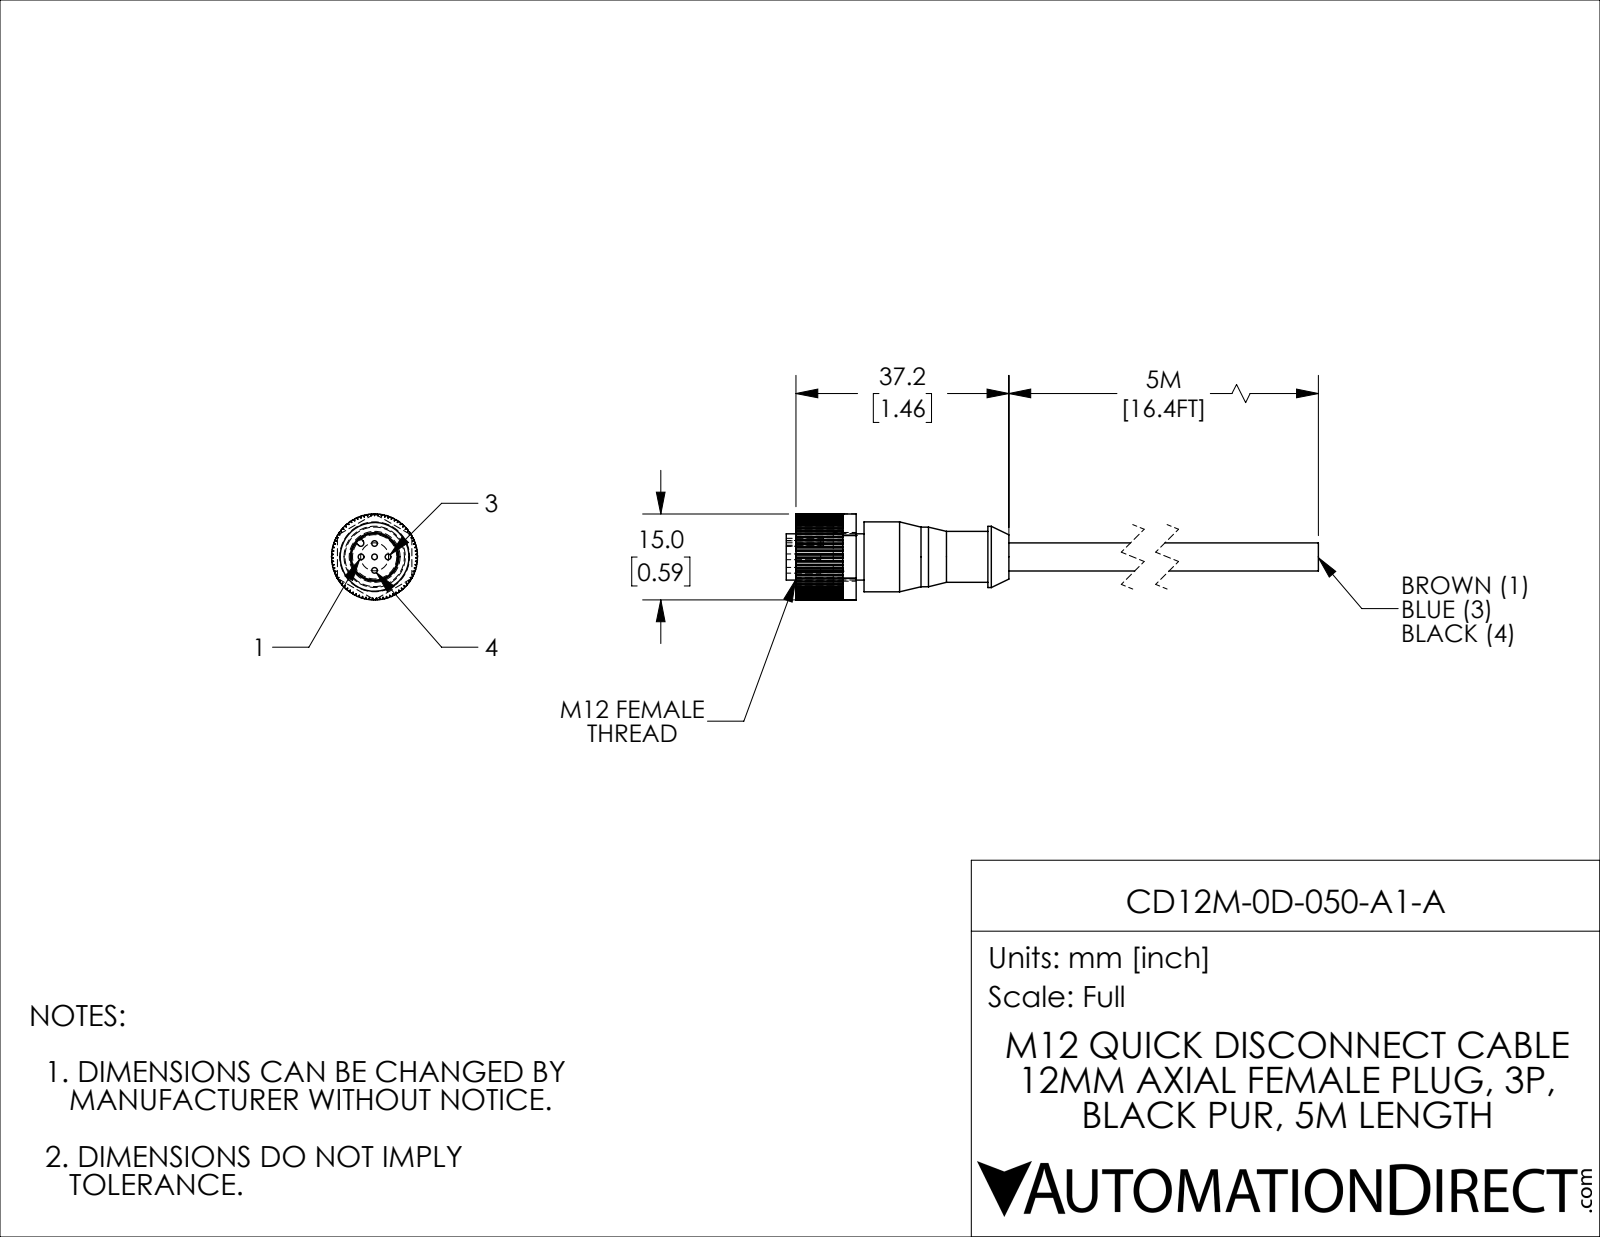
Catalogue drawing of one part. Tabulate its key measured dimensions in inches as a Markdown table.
| quantity | value |
| --- | --- |
| part name | CD12M-0D-050-A1-A |
| STEP written by | SolidWorks 2021 (CONFIG_CONTROL_DESIGN) |
| units | inches |
| bodies | 4 solids, 308 faces (195 planar, 107 cylindrical, 6 other) |
| overall size | 5.469 × 0.591 × 0.591 |
| volume | 0.336 in³ |
| surface area | 6.948 in² |
| round holes (diameter × count) | 0.039 × 5, 0.335 × 1, 0.472 × 1 |
| round bosses / shafts (diameter × count) | 0.48 × 1, 0.421 × 1, 0.409 × 1, 0.35 × 1, 0.319 × 1, 0.193 × 1 |
| partial cylindrical surfaces (radius × count) | 0.022 × 1, 0.295 × 1 |
| main face-to-face distances | 0.996, 0.055, 0.067, 0.323, 1.051, 1.465, 0.469, 0.413, 0.256, 1.209 |
| hole center spacings | 0.093, 0.131, 0.185 |
